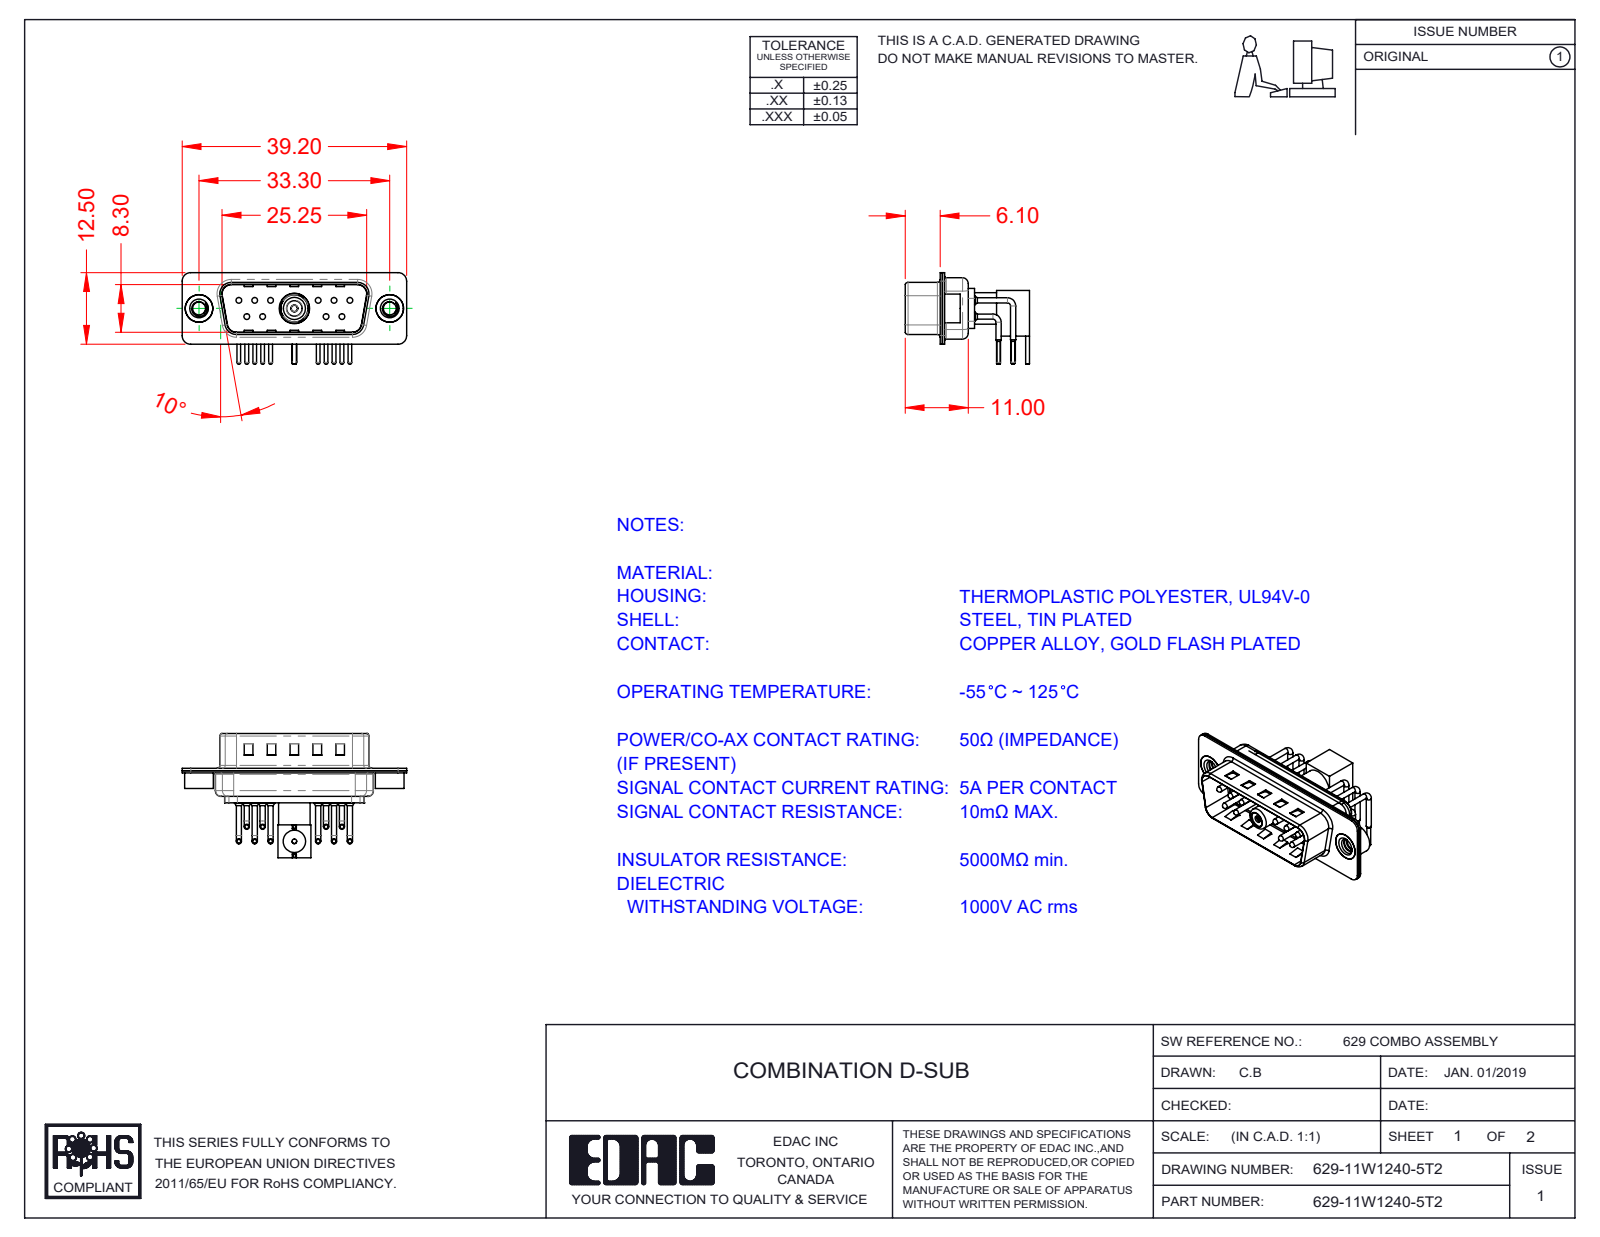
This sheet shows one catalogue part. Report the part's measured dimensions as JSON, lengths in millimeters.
{"part_name": "629Combo Shell Front_15 Contacts; Socket_RA; Locking Collar; 629-11W1240-5T2 (+8 more)", "step_written_by": "SolidWorks 2020 (CONFIG_CONTROL_DESIGN)", "units": "millimeters", "bodies": {"solids": 22, "faces": 1605, "planar": 845, "cylindrical": 564, "other": 196}, "overall_size": [39.2, 21.71, 16], "volume_mm3": 2212, "surface_area_mm2": 6078, "round_holes": [[1.6, 11], [0.75, 10], [2, 10], [2.26, 2], [4, 2], [4.8, 2], [0.8, 1], [1.1, 1], [1.2, 1], [1.5, 1], [2.5, 1], [2.7, 1]], "round_bosses_or_shafts": [[0.9, 20], [1.5, 10], [1, 10], [0.65, 10], [5, 2], [4.9, 2], [0.8, 2], [5.5, 1]], "partial_cylinders_radius": [[1.5, 16], [2, 12], [1.01, 10], [0.5, 8], [1.6, 8], [1, 7], [0.25, 4], [0.6, 4]], "face_to_face_distances": [0.4, 0.8, 9.5, 9.1, 8.7, 0.35, 9.9, 0.75, 1.2, 1.4], "hole_center_spacings": [3.16, 2.77, 13.85, 11.08, 16.62, 5.03, 5.04, 5.54]}
